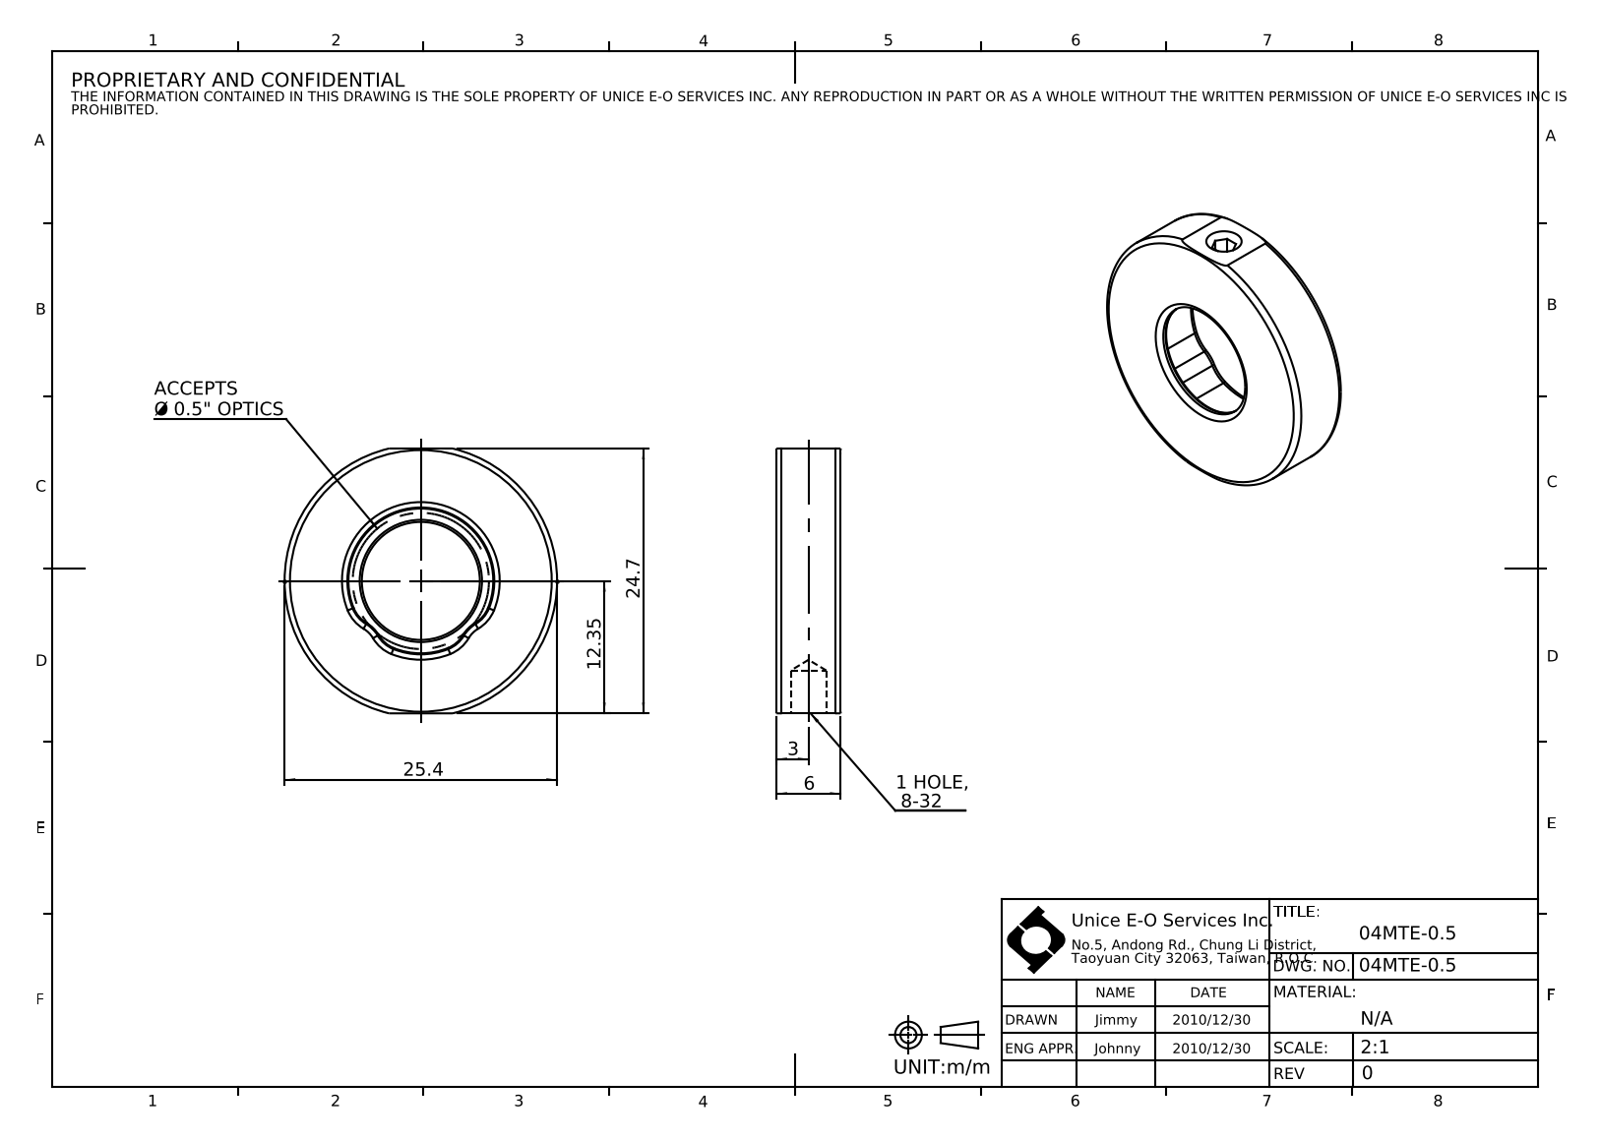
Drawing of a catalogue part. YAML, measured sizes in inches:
part_name: "04MTE-0.5"
step_written_by: "SolidWorks 2016 (CONFIG_CONTROL_DESIGN)"
units: inches
bodies: {solids: 3, faces: 77, planar: 16, cylindrical: 25, other: 36}
overall_size: [1, 0.972, 0.236]
volume: 0.131
surface_area: 2.618
round_holes:
  - {diameter: 0.059, count: 1}
  - {diameter: 0.13, count: 1}
  - {diameter: 0.136, count: 1}
  - {diameter: 0.433, count: 1}
round_bosses_or_shafts:
  - {diameter: 1, count: 1}
  - {diameter: 0.157, count: 1}
  - {diameter: 0.063, count: 1}
partial_cylinders:
  - {radius: 0.118, count: 6}
  - {radius: 0.27, count: 1}
face_to_face_distances: [0.236, 0.039, 0.197, 0.972, 0.079, 0.157, 0.953, 0.02, 0.795, 0.177]
